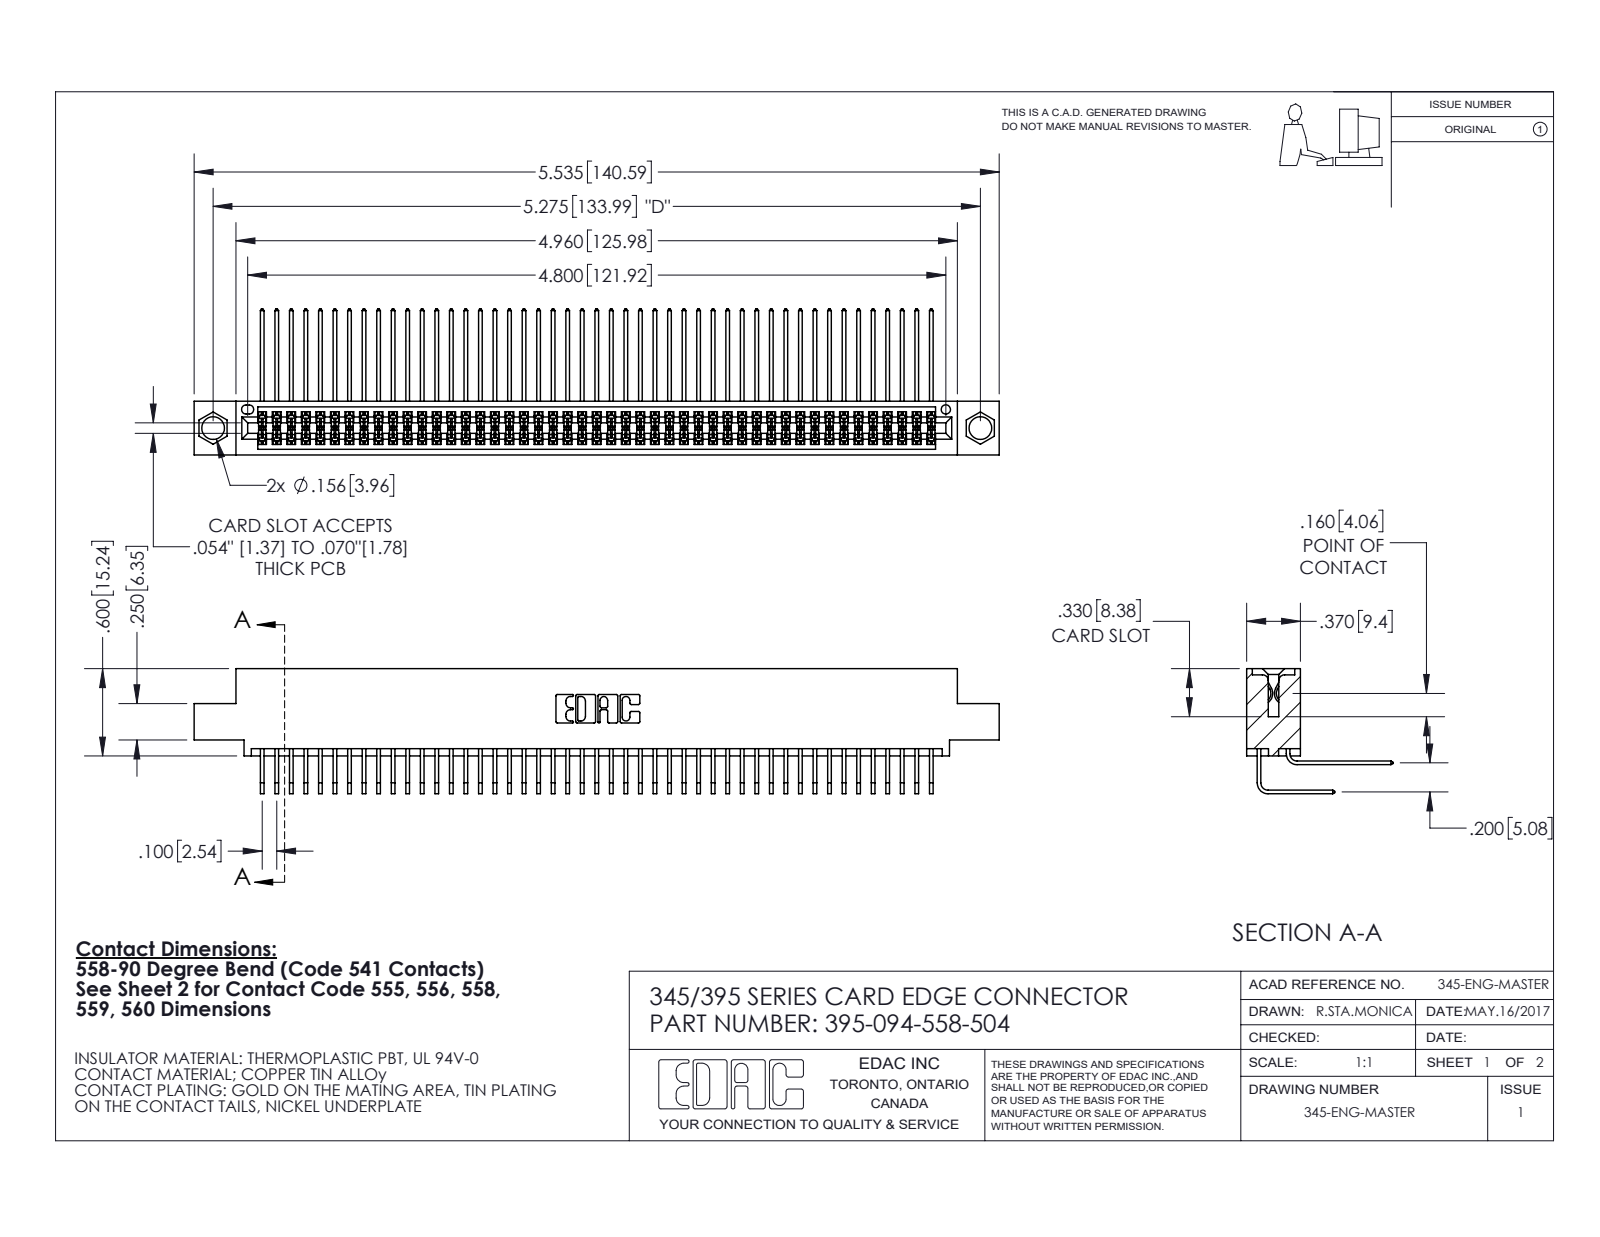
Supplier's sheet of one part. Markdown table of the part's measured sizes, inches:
| quantity | value |
| --- | --- |
| part name | 345-292-001_558 Tail - 2; 345 Part_0.110 Offset - 0.156 Dia-TI; 345-292-001_558 559 Tail - 1; 395-094-558-504 |
| STEP written by | SolidWorks 2020 (CONFIG_CONTROL_DESIGN) |
| units | inches |
| bodies | 95 solids, 5032 faces (3388 planar, 1644 cylindrical, 0 other) |
| overall size | 5.535 × 1.005 × 0.859 |
| volume | 0.858 in³ |
| surface area | 36.24 in² |
| round holes (diameter × count) | 0.156 × 2, 0.064 × 1 |
| partial cylindrical surfaces (radius × count) | 0.006 × 188, 0.01 × 22, 0.007 × 6, 0.031 × 6, 0.026 × 3, 0.014 × 2, 0.019 × 2, 0.022 × 2 |
| main face-to-face distances | 0.072, 0.298, 0.2, 0.37, 0.098, 0.272, 0.025, 0.225, 0.025, 0.175 |
| hole center spacings | 0.27, 5.039, 5.275 |
